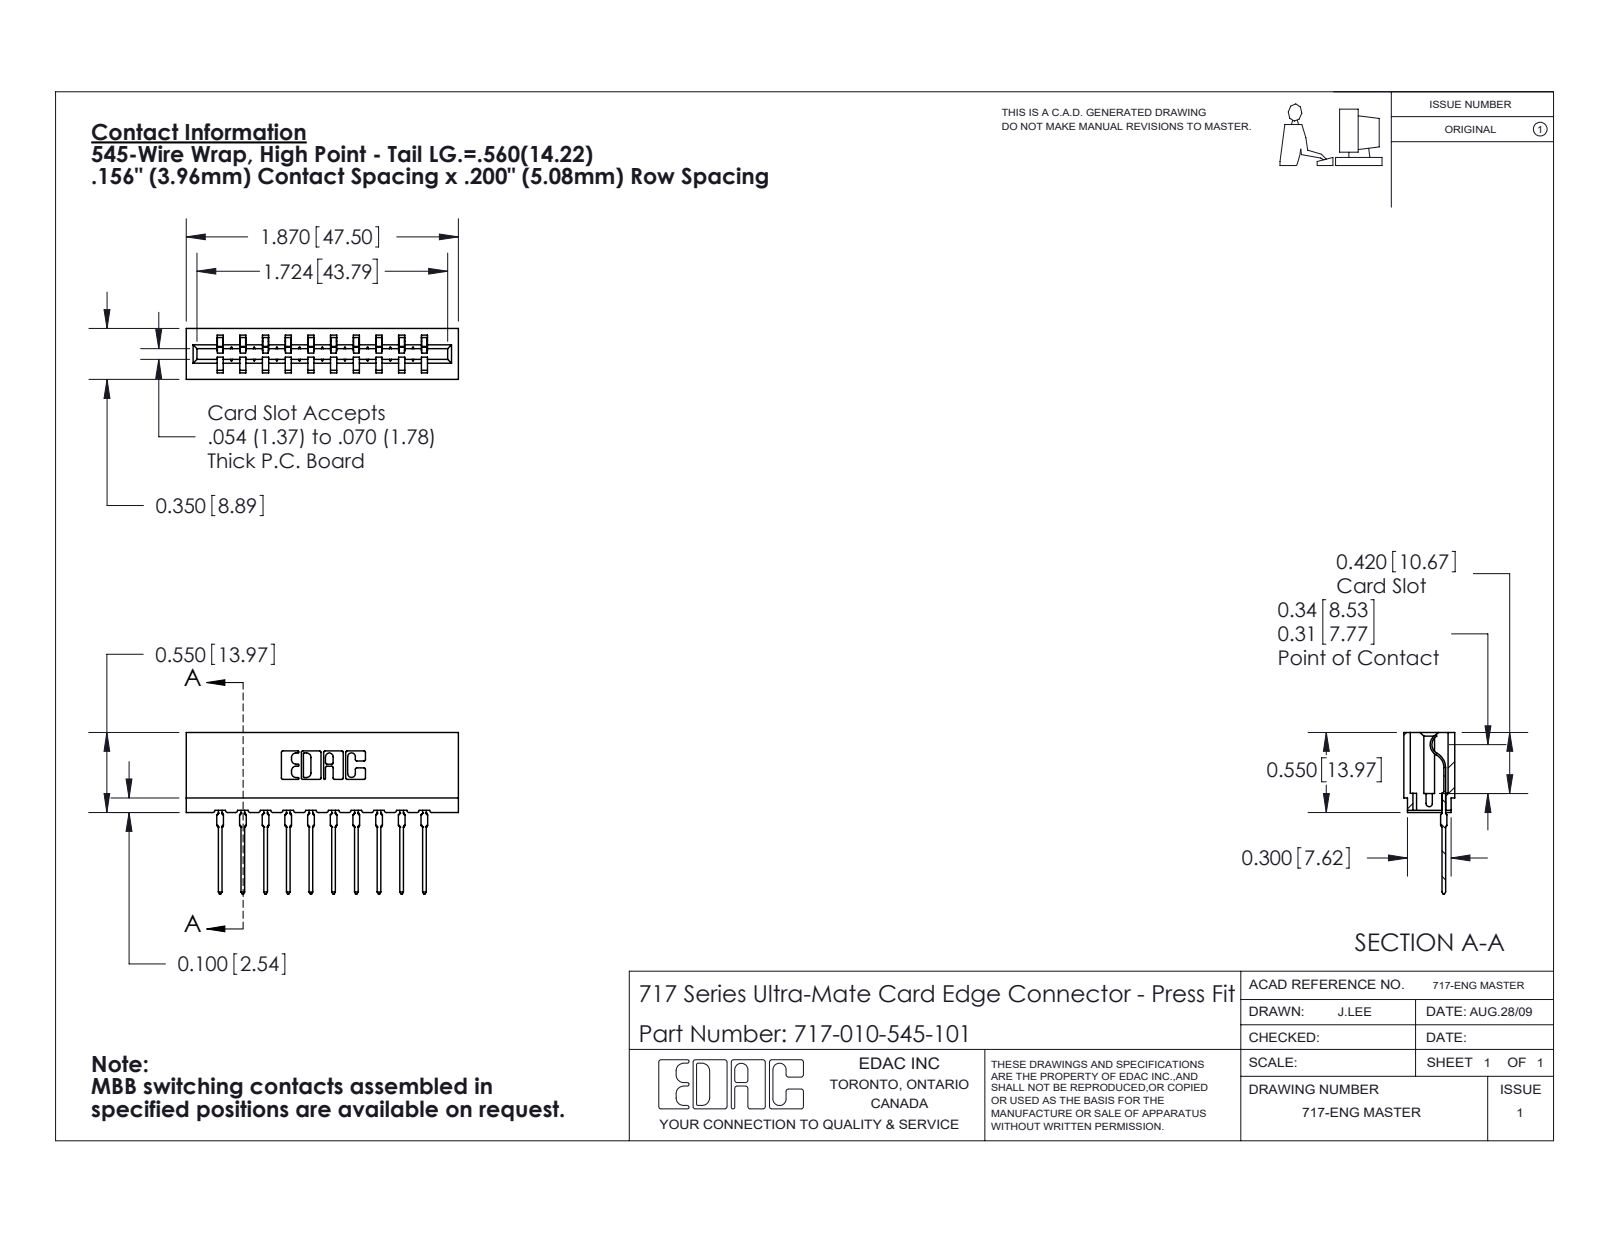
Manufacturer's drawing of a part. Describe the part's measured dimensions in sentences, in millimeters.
The part is named "717 Part_Insulator Option - 06; 717-010-545-101; 745-292-001_545". Its 3-D file was written by "SolidWorks 2020 (CONFIG_CONTROL_DESIGN)". It is 11 solids with 1224 faces: 734 planar, 230 cylindrical and 260 other. Overall it measures 47.5 by 28.2 by 8.9 millimeters. Its volume is 4 180 cubic millimeters and its surface area 5 686 square millimeters. Partial cylindrical surfaces (rounded edges, fillets, slot ends): 22 of radius 0.3, 20 of radius 0.4, 20 of radius 0.5, 6 of radius 0.2, 6 of radius 0.8, 4 of radius 0.1, 4 of radius 0.3, 3 of radius 0.7. The main face-to-face distances are 4, 5.4, 3.5, 15.8, 8.9, 5, 11.9, 7.9, 9, 7.9.
